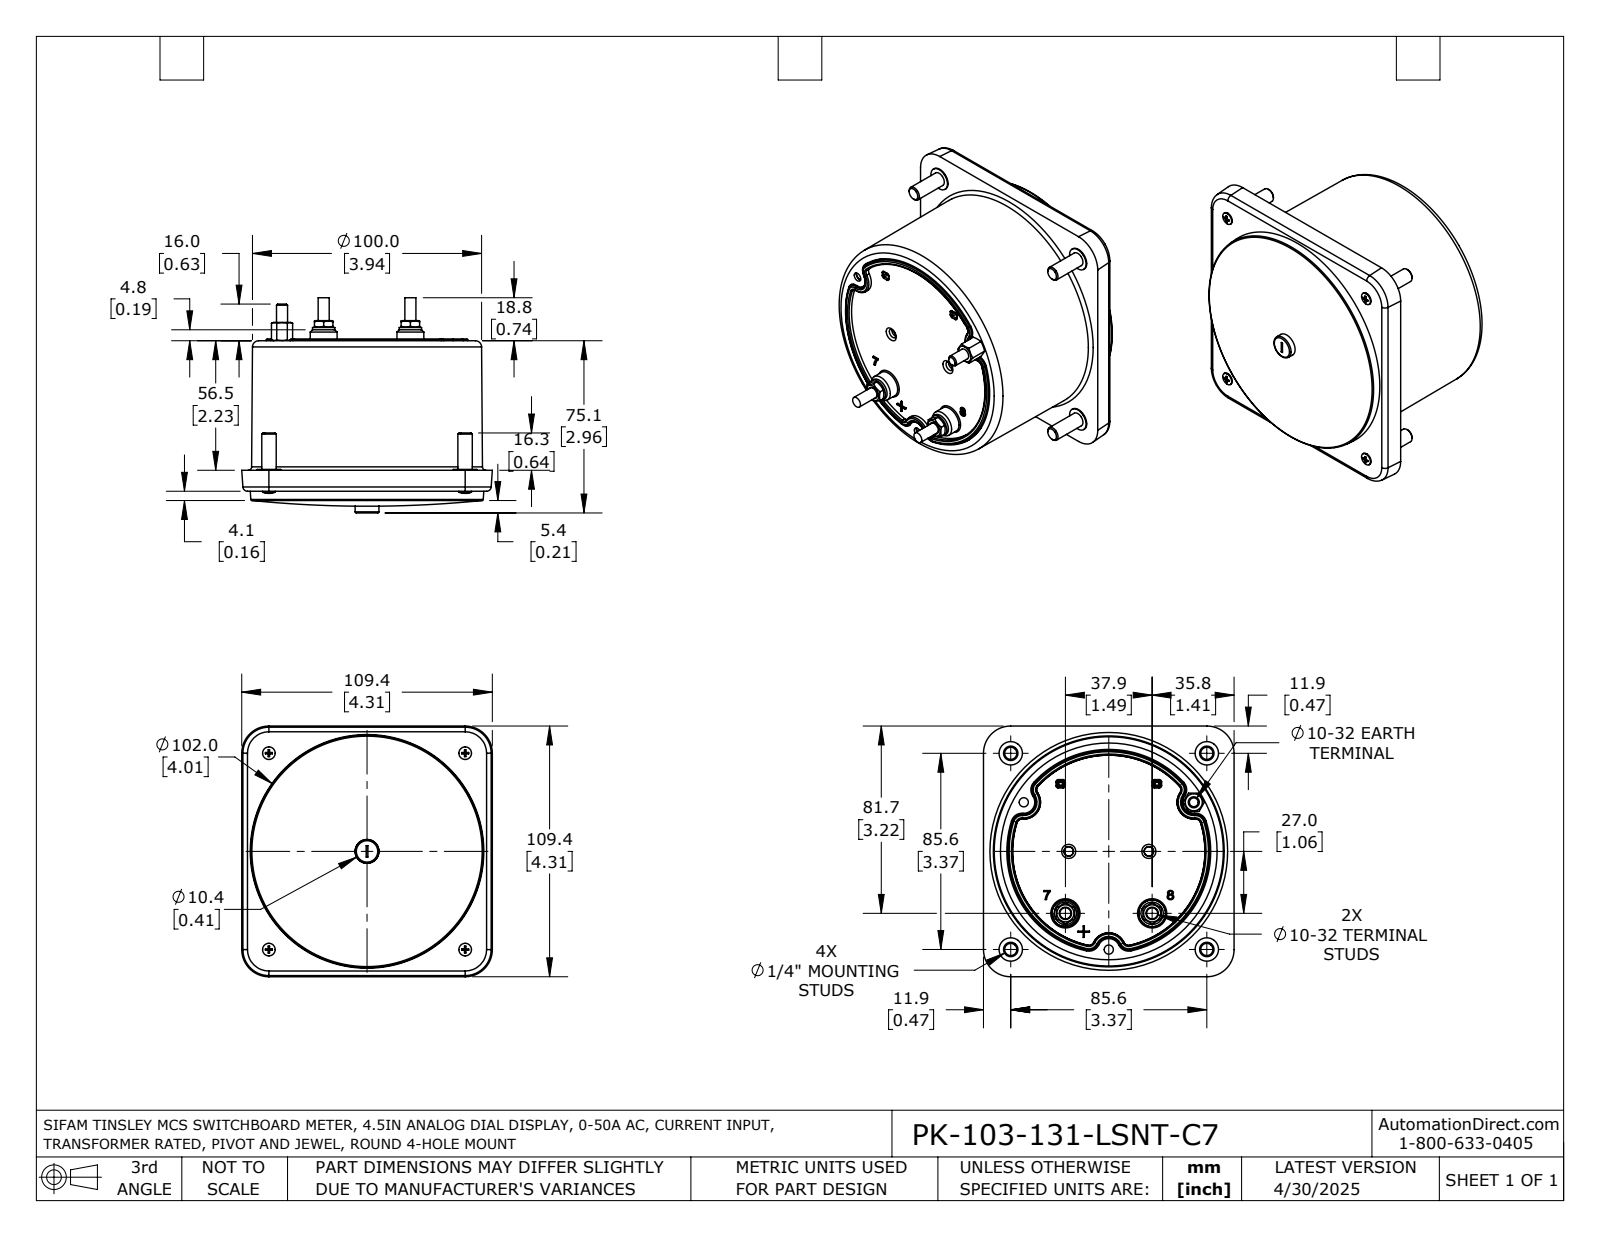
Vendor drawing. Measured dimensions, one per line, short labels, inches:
name: PK-103-131-LSNT-C7
written by: SolidWorks 2021 (AUTOMOTIVE_DESIGN)
unit: in
bodies: 1 solid, 609 faces (167 planar, 141 cylindrical, 301 other)
size: 4.307 × 4.307 × 3.697
volume: 36.28 in³; area: 82.21 in²
holes: 4× ⌀0.094, 4× ⌀0.138, 4× ⌀0.315, 3× ⌀0.157, 2× ⌀0.209
bosses: 4× ⌀0.402, 4× ⌀0.248, 4× ⌀0.217, 4× ⌀0.114, 3× ⌀0.19, 2× ⌀0.384, 1× ⌀0.146
rounds: 24× R0.02, 9× R0.189, 4× R0.079, 1× R1.752
face distances: 2.177, 2.537, 0.36, 0.048, 2.225, 2.585, 0.489, 2.715, 2.667, 0.129
hole spacings: 3.372, 3.37, 3.374, 3.378, 3.38, 4.769, 0.971, 1.126
